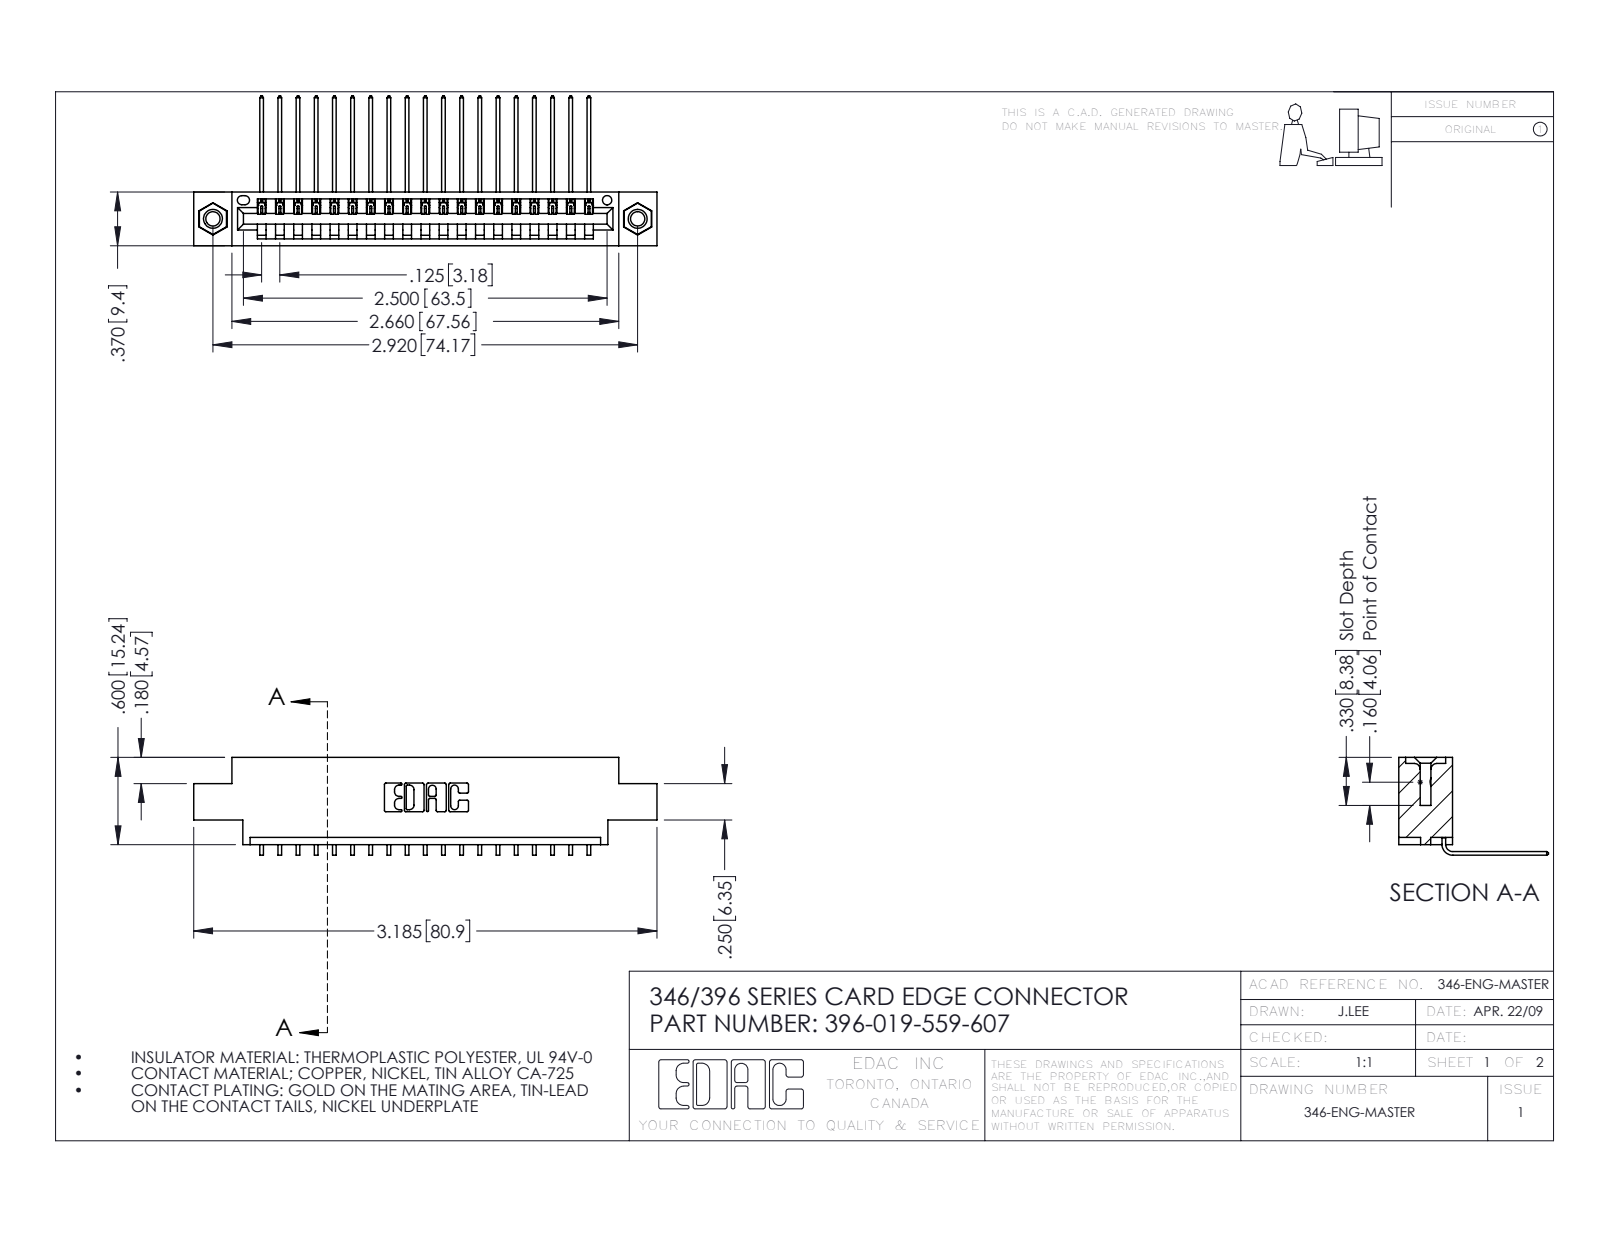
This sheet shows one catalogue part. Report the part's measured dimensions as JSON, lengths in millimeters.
{"part_name": "396-019-559-607; 345-292-001_558 559 Tail - 1; 346 Part_0.170 Offset - 0.156 Dia-TI; 345-250-001_345-250-005-103", "step_written_by": "SolidWorks 2016 (CONFIG_CONTROL_DESIGN)", "units": "millimeters", "bodies": {"solids": 22, "faces": 1326, "planar": 910, "cylindrical": 400, "other": 16}, "overall_size": [80.9, 26.2, 17.1], "volume_mm3": 7470, "surface_area_mm2": 9671, "round_holes": [[2.5, 2], [3.2, 2], [4, 2], [1.6, 1]], "round_bosses_or_shafts": [[3.9, 2]], "partial_cylinders_radius": [[0.2, 38], [0.3, 22], [0.2, 6], [0.8, 6], [0.7, 3], [0.8, 2], [1, 2], [0.4, 1]], "face_to_face_distances": [1.2, 9.4, 8.2, 6.4, 0.6, 1.8, 5.6, 3.8, 2.5, 4.4], "hole_center_spacings": [6.2, 68.9, 74.2]}
